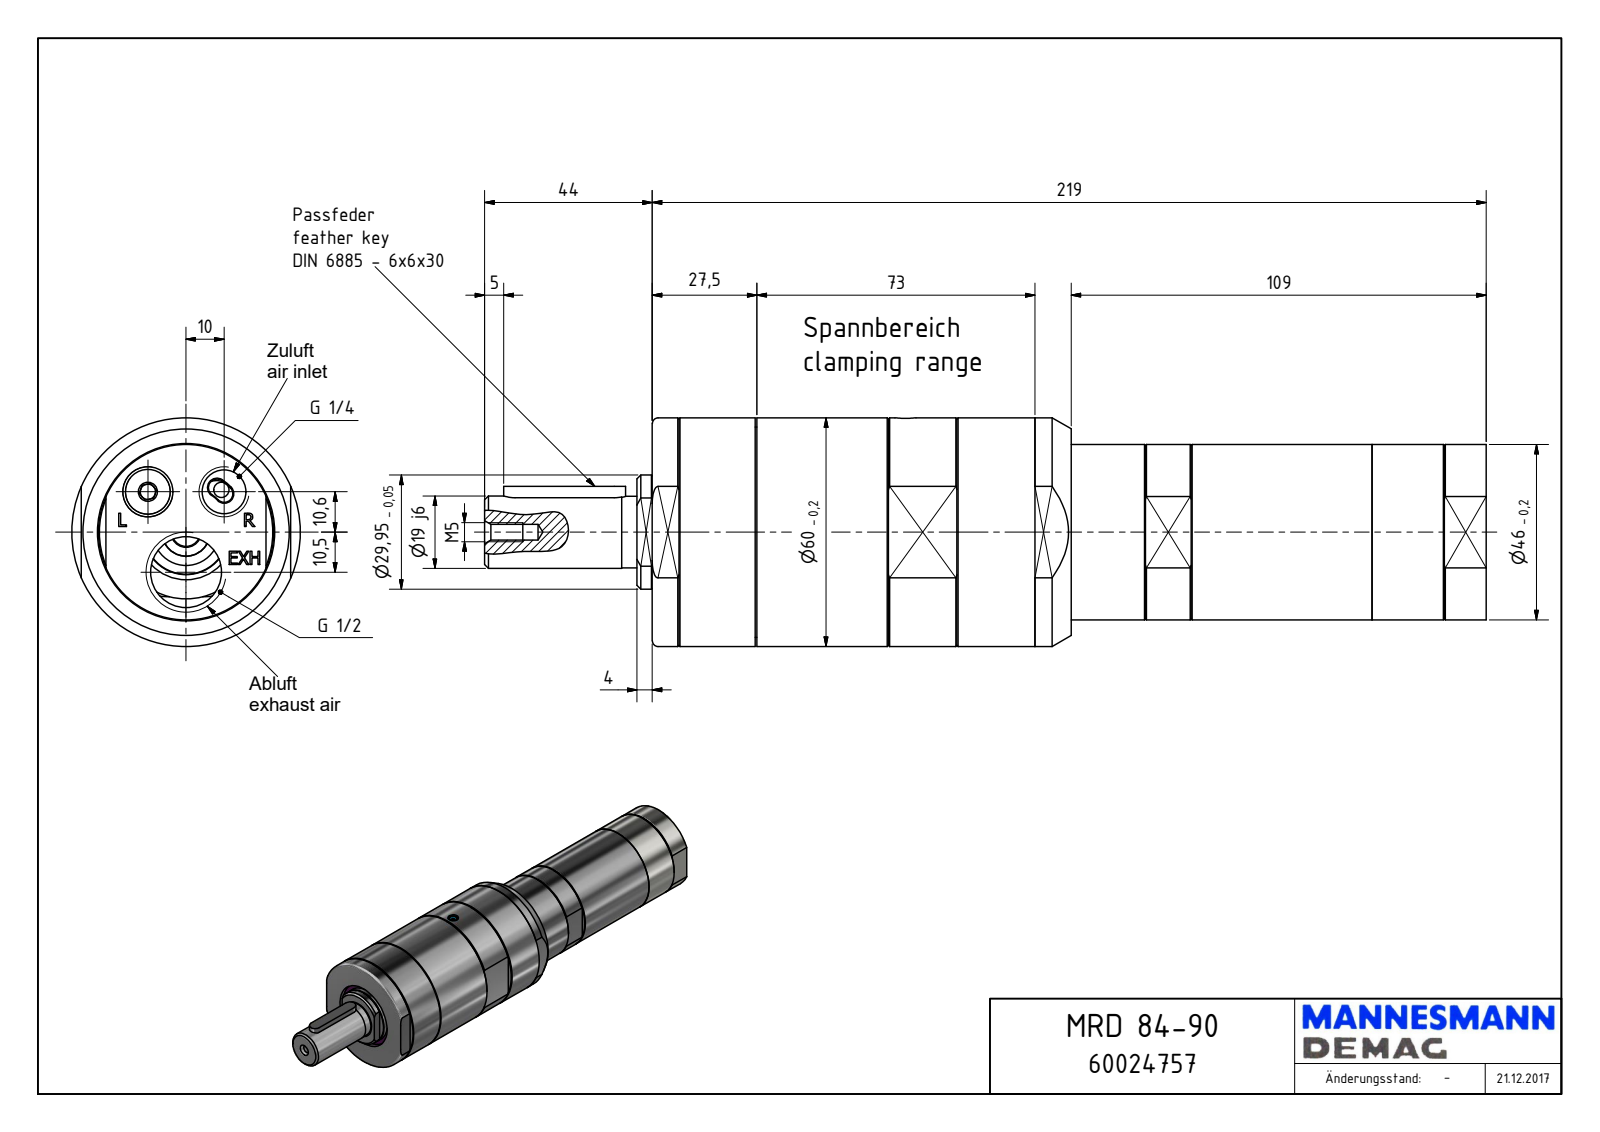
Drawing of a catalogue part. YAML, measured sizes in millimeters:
part_name: "MRD 84-90_60024757"
step_written_by: "Autodesk Inventor 2018 (AUTOMOTIVE_DESIGN)"
units: millimeters
bodies: {solids: 1, faces: 241, planar: 133, cylindrical: 58, other: 50}
overall_size: [263, 60, 60]
volume: 496048
surface_area: 51593
round_holes:
  - {diameter: 4, count: 2}
  - {diameter: 1.55, count: 1}
  - {diameter: 4.13, count: 1}
  - {diameter: 5.5, count: 1}
  - {diameter: 11.45, count: 1}
  - {diameter: 18.63, count: 1}
  - {diameter: 35, count: 1}
  - {diameter: 42, count: 1}
  - {diameter: 46.5, count: 1}
  - {diameter: 55.38, count: 1}
round_bosses_or_shafts:
  - {diameter: 60, count: 1}
  - {diameter: 55.18, count: 1}
  - {diameter: 46, count: 1}
  - {diameter: 41.99, count: 1}
  - {diameter: 32.65, count: 1}
  - {diameter: 29.95, count: 1}
  - {diameter: 19, count: 1}
  - {diameter: 18.8, count: 1}
partial_cylinders:
  - {radius: 2.5, count: 4}
  - {radius: 3, count: 2}
  - {radius: 5, count: 2}
  - {radius: 5.72, count: 1}
  - {radius: 16.75, count: 1}
  - {radius: 19, count: 1}
  - {radius: 27.28, count: 1}
  - {radius: 28.35, count: 1}
face_to_face_distances: [219, 6.5, 48.5, 55, 110, 109, 27.5, 82.5, 191.5, 42]
hole_center_spacings: [14.57, 23.35, 10.5, 20]
